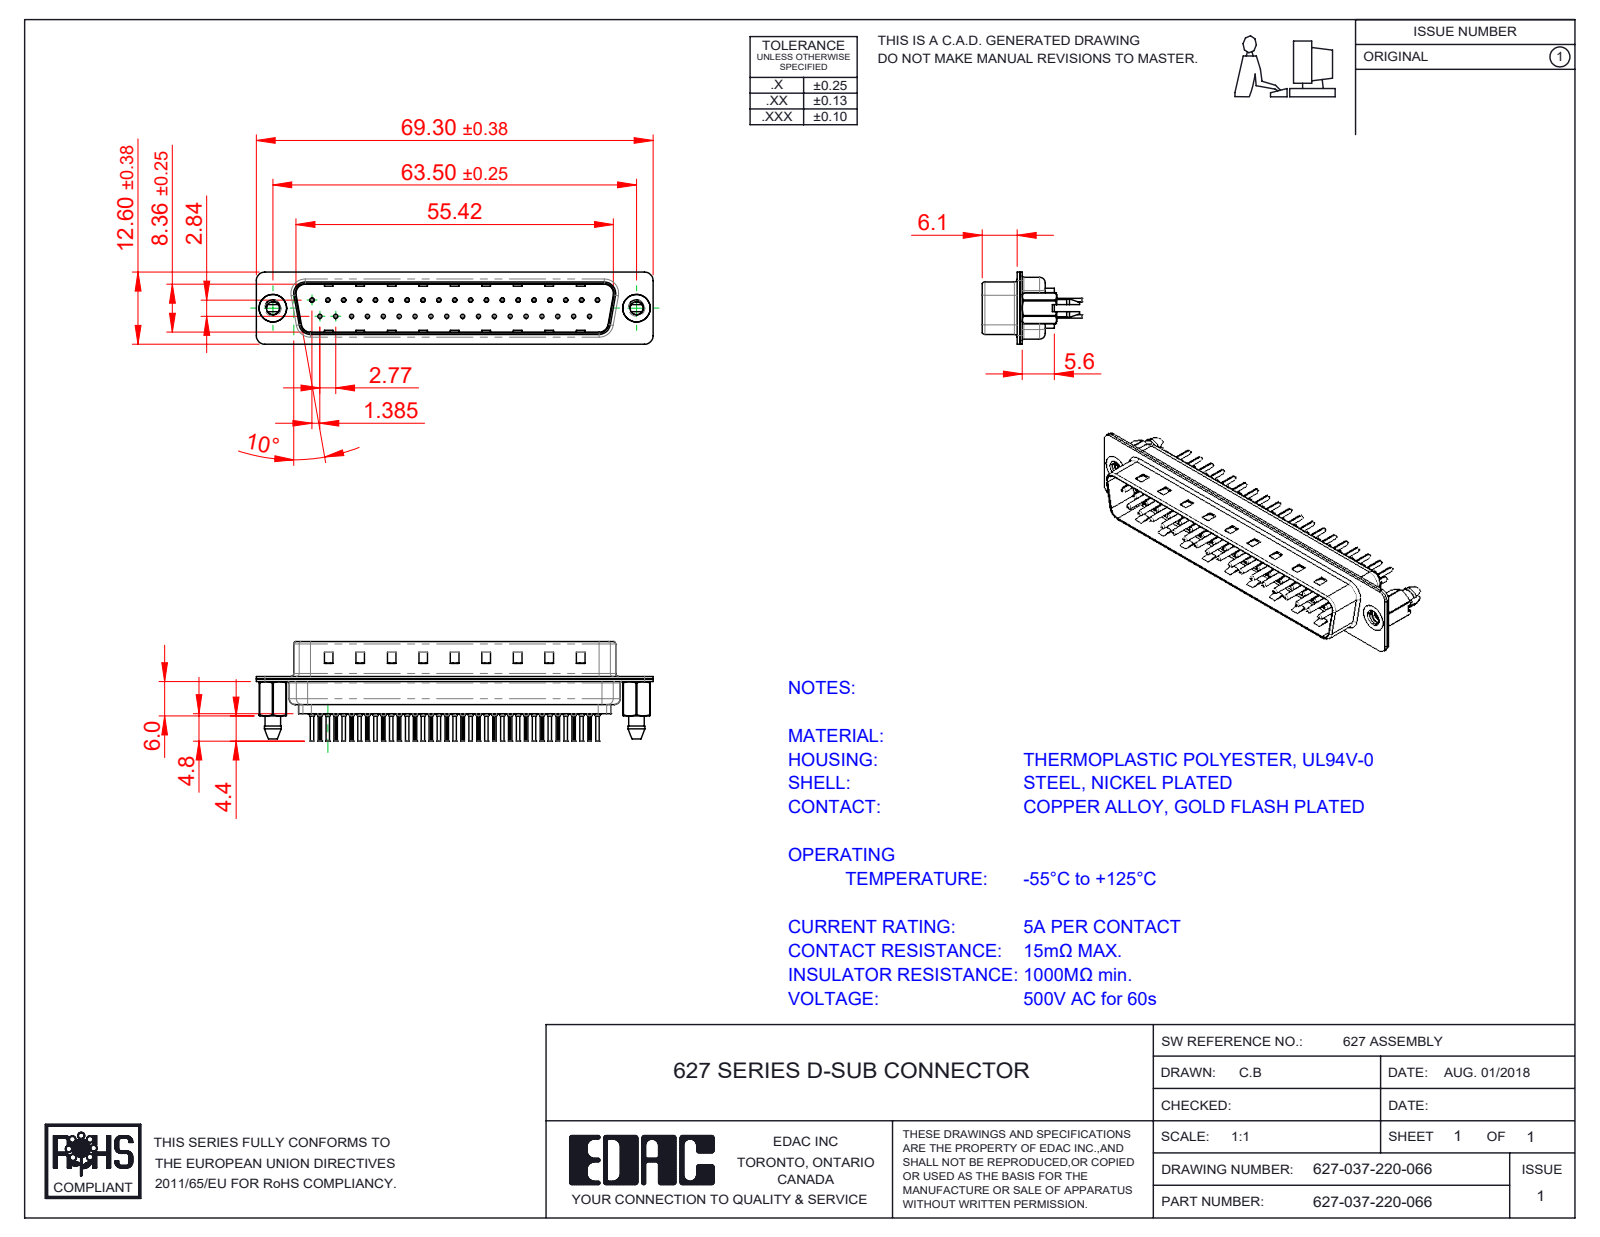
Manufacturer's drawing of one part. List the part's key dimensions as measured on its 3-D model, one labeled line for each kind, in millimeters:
Part name (STEP PRODUCT): 627 Shell Front_37 Contacts; 627 Contact Row 1_20L; 627 4-40 Threaded Boardlock_LP; 627 Contact Row 2_20L (+3 more)
STEP written by: SolidWorks 2020 (CONFIG_CONTROL_DESIGN)
Units: millimetres
Bodies: 42 solids, 4112 faces (1123 planar, 1542 cylindrical, 1447 other)
Overall size (bounding box): 69.3 × 17.3 × 12.6
Volume: 3 816 mm³ · Surface area: 10 972 mm²
Round holes (diameter × count): ⌀0.2 ×37, ⌀0.35 ×37, ⌀1.1 ×37, ⌀1.6 ×37, ⌀2.26 ×2, ⌀4 ×2, ⌀4.8 ×2
Round bosses / shafts (diameter × count): ⌀2 ×37, ⌀1.5 ×37, ⌀0.75 ×37, ⌀0.6 ×37, ⌀4.9 ×2
Partial cylindrical surfaces — rounded edges, fillets, slot ends (radius × count): R0.1 ×74, R1.5 ×18, R2 ×12, R1.6 ×10, R0.5 ×8, R0.25 ×4, R0.6 ×4, R0.65 ×4
Main face-to-face distances: 0.4, 0.82, 9.58, 0.45, 8.76, 1.5, 0.9, 1.4, 6.5, 6.05
Hole centre spacings: 3.16, 2.77, 5.54, 8.31, 5.04, 10.1, 11.08, 12.78
